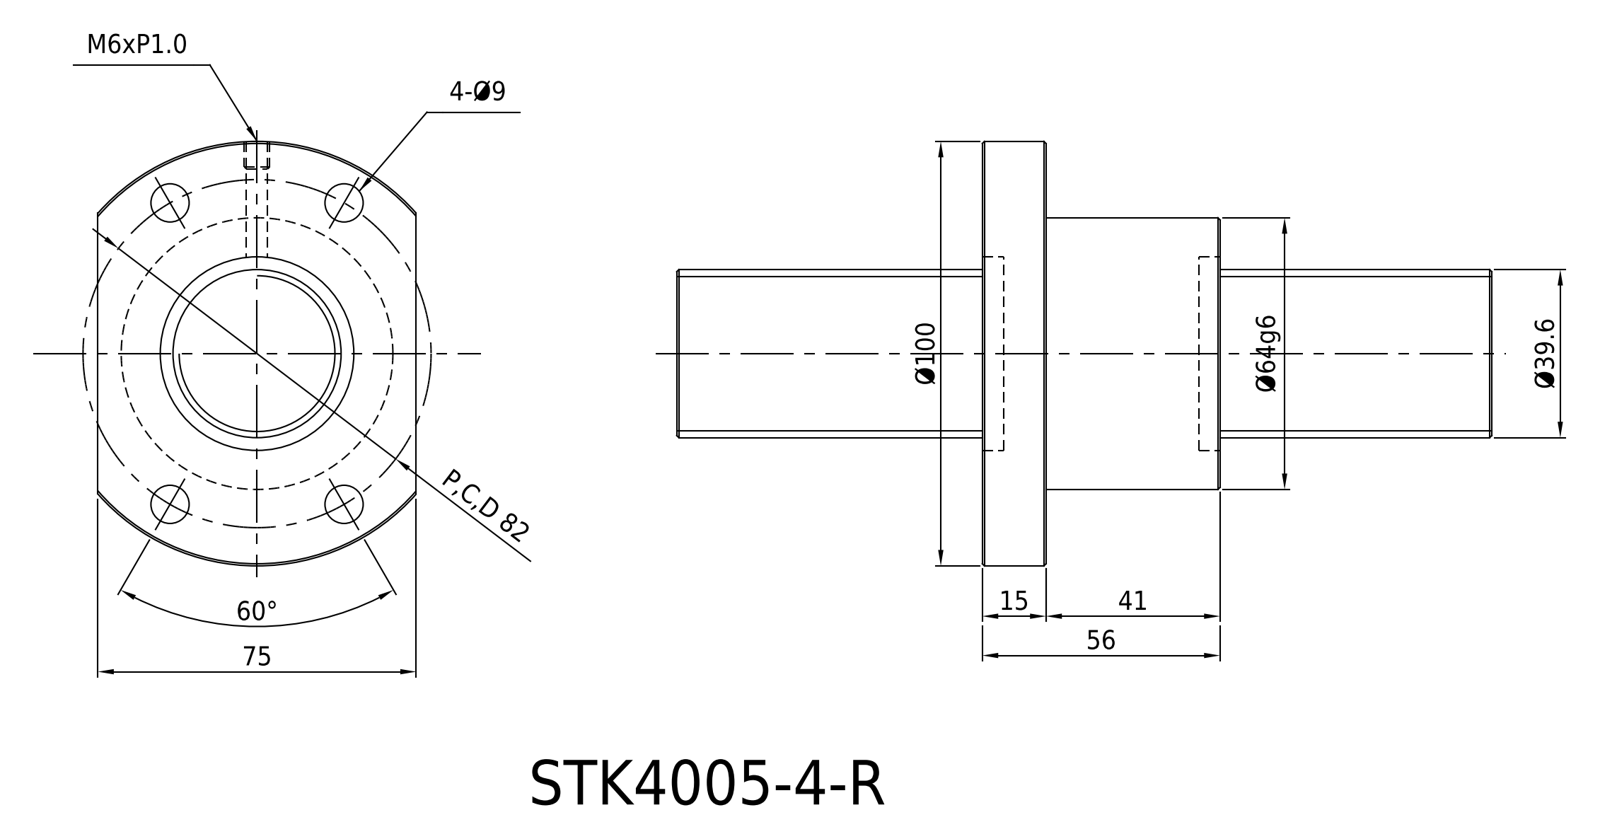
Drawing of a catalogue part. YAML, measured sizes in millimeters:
part_name: "4005 STK"
step_written_by: "CATIA V5 STEP AP214 (AUTOMOTIVE_DESIGN)"
units: millimeters
bodies: {solids: 1, faces: 45, planar: 5, cylindrical: 14, other: 26}
overall_size: [100, 75, 56]
volume: 158390
surface_area: 31628
round_holes:
  - {diameter: 9, count: 4}
  - {diameter: 40, count: 1}
round_bosses_or_shafts:
  - {diameter: 64, count: 1}
partial_cylinders:
  - {radius: 50, count: 1}
face_to_face_distances: [15, 41, 56, 75]
hole_center_spacings: [41, 71.02, 82.01]
